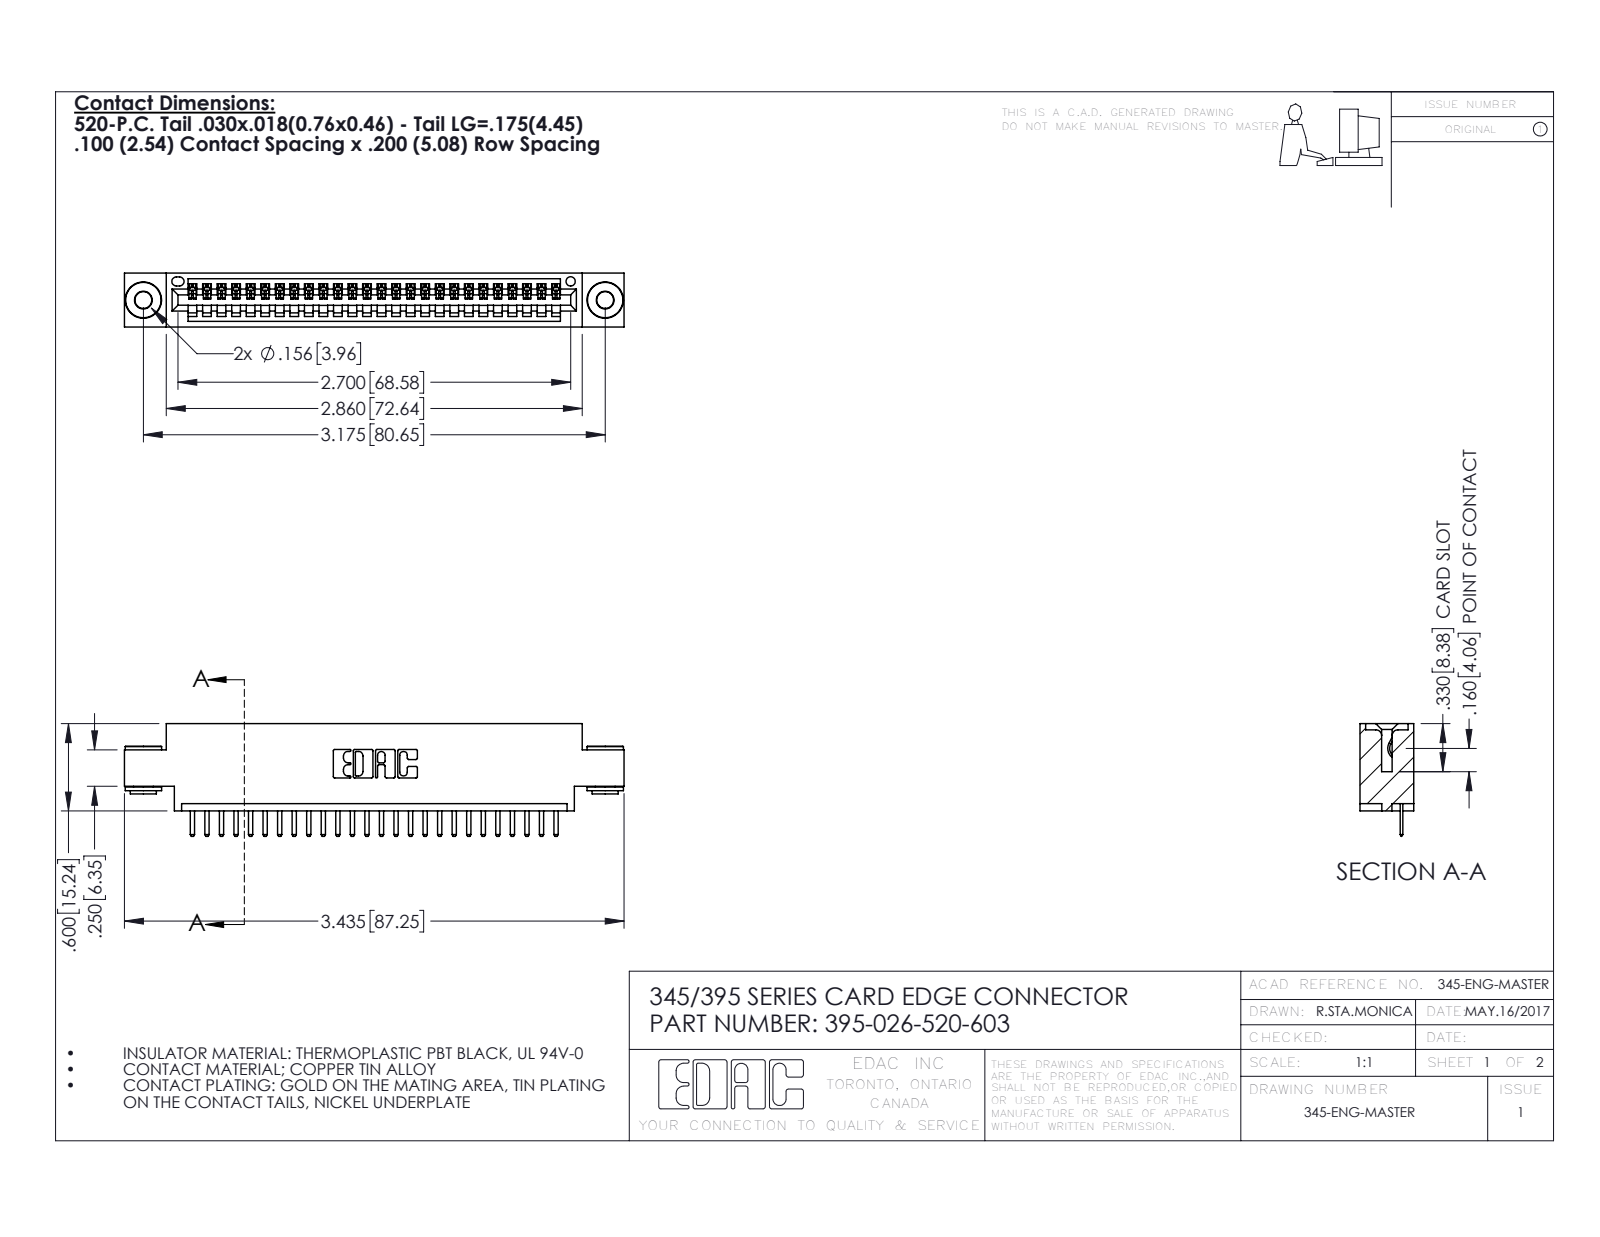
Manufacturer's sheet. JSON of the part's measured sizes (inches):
{"part_name": "395-026-520-603; 345-250-002_345-250-002-102; 345-292-001_345-293-120; 345 Part_0.170 Offset - 0.156 Dia-TH", "step_written_by": "SolidWorks 2016 (CONFIG_CONTROL_DESIGN)", "units": "inches", "bodies": {"solids": 29, "faces": 1780, "planar": 1186, "cylindrical": 586, "other": 8}, "overall_size": [3.435, 0.775, 0.37], "volume_in3": 0.487, "surface_area_in2": 16.26, "round_holes": [[0.116, 2], [0.156, 2], [0.064, 1]], "round_bosses_or_shafts": [[0.25, 2], [0.18, 2], [0.136, 2]], "partial_cylinders_radius": [[0.01, 54], [0.006, 52], [0.01, 22], [0.007, 6], [0.031, 6], [0.026, 3], [0.031, 2], [0.04, 2]], "face_to_face_distances": [0.072, 0.298, 0.37, 0.2, 0.098, 0.272, 0.025, 0.225, 0.175, 0.072], "hole_center_spacings": [0.27, 2.94, 3.175]}
